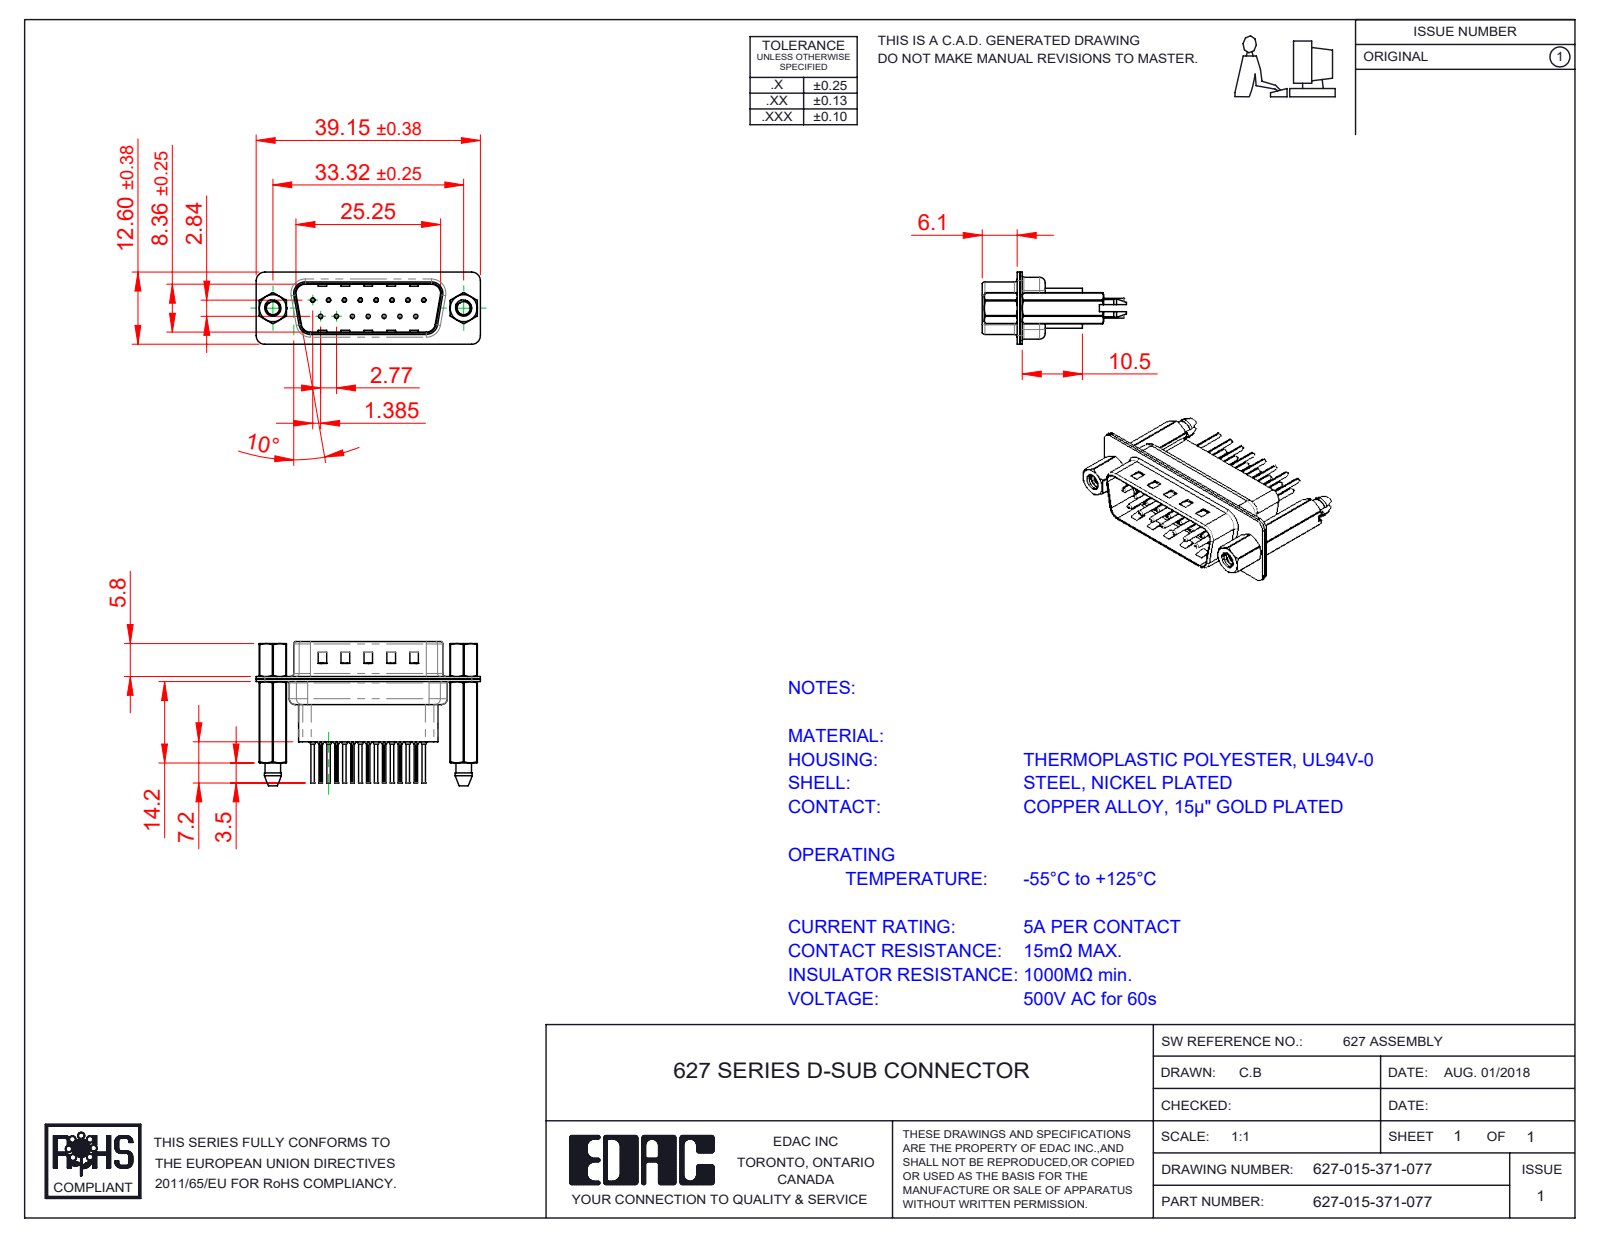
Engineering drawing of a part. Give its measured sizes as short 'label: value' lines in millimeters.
name: 627 Shell Rear_15 Contacts; 627 Housing_15 HP; 627 Contact Row 2_61; 627 Contact Row 1_61 (+4 more)
written by: SolidWorks 2020 (CONFIG_CONTROL_DESIGN)
unit: mm
bodies: 22 solids, 2044 faces (553 planar, 826 cylindrical, 665 other)
size: 39.15 × 25.1 × 12.6
volume: 3 123 mm³; area: 8 000 mm²
holes: 15× ⌀0.2, 15× ⌀0.35, 15× ⌀1.1, 15× ⌀1.6, 2× ⌀2.26, 2× ⌀2.29, 2× ⌀4, 2× ⌀4.8
bosses: 15× ⌀2, 15× ⌀1.5, 15× ⌀0.75, 15× ⌀0.6, 2× ⌀4.9, 2× ⌀2.79
rounds: 30× R0.1, 18× R1.5, 12× R2, 10× R1.6, 8× R0.5, 4× R0.25, 4× R0.6, 4× R0.65
face distances: 0.4, 0.45, 4.76, 0.9, 0.82, 9.58, 1.5, 0.68, 7.68, 16.66
hole spacings: 3.16, 2.77, 5.54, 8.31, 11.08, 5.03, 5.04, 7.48
